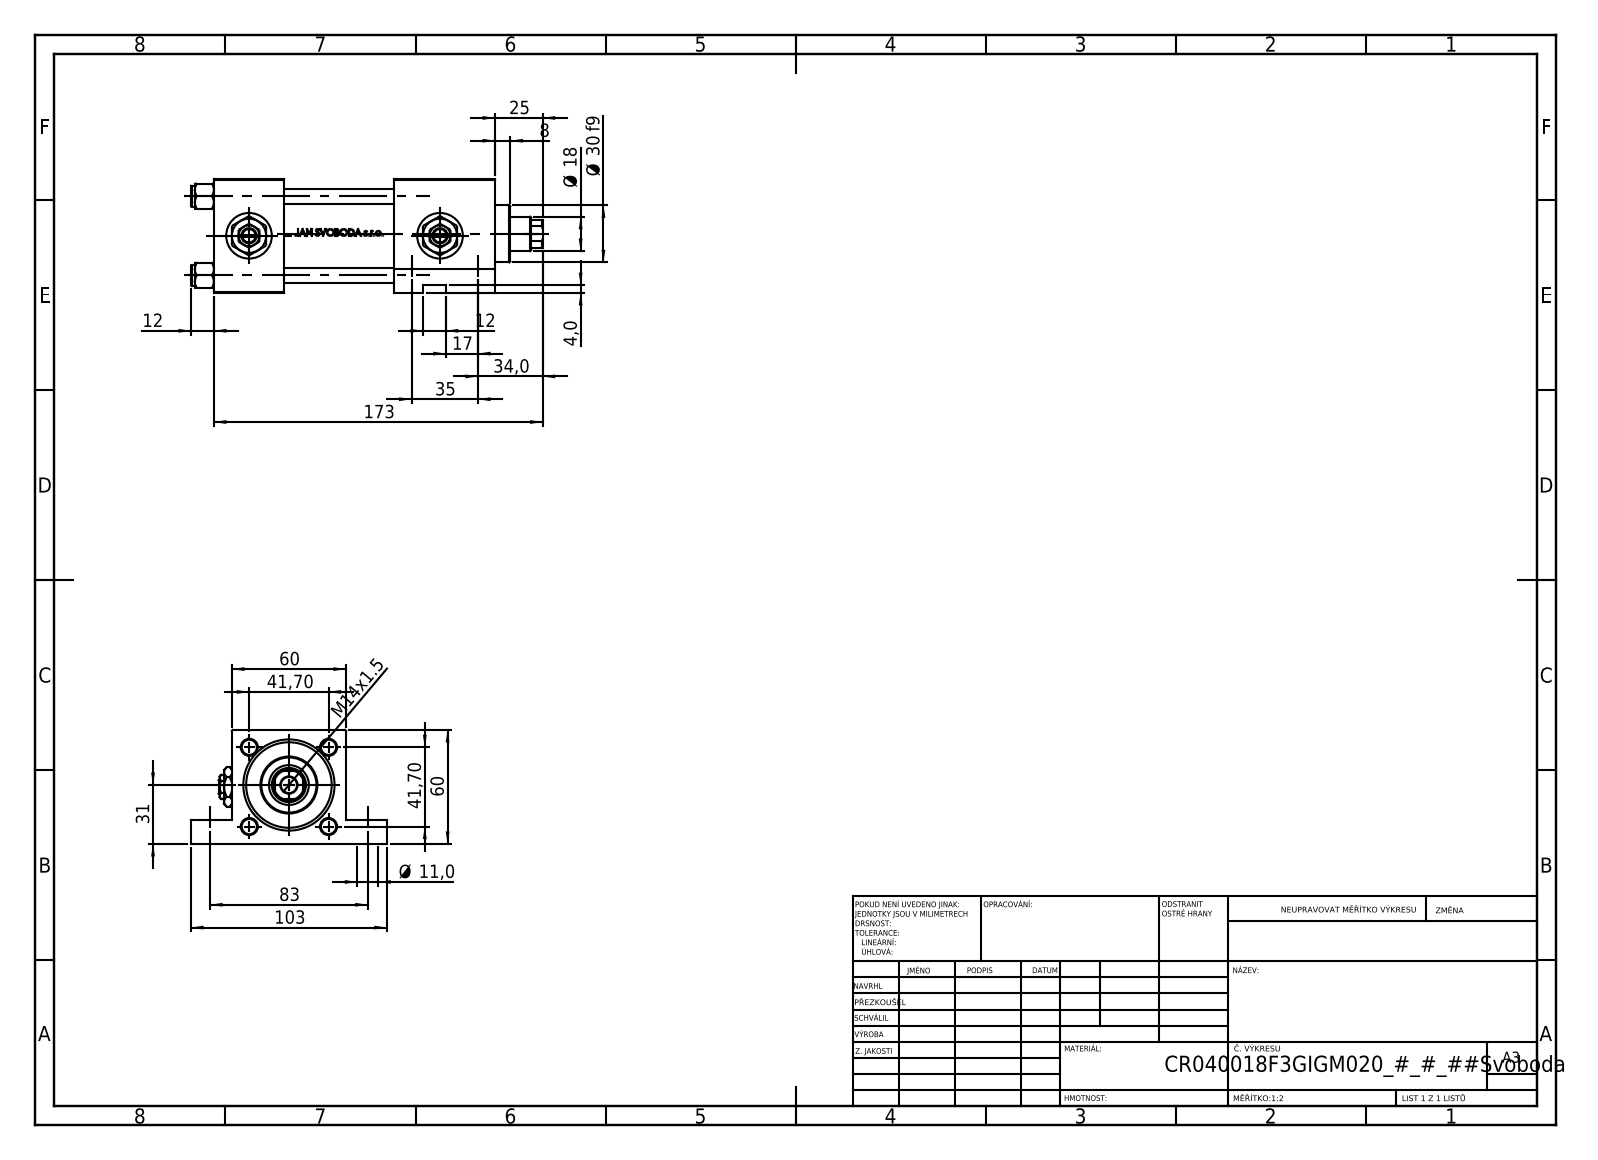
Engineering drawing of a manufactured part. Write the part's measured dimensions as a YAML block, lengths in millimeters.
part_name: "V215CR_VCP_F; V215CR_F_TYCINKA; V215_VC_A; V215CR_F_Body (+2 more)"
step_written_by: "SolidWorks 2019 (CONFIG_CONTROL_DESIGN)"
units: millimeters
bodies: {solids: 13, faces: 1215, planar: 484, cylindrical: 149, other: 582}
overall_size: [185, 103, 60]
volume: 420373
surface_area: 114469
round_holes:
  - {diameter: 8, count: 4}
  - {diameter: 16.66, count: 3}
  - {diameter: 24, count: 3}
  - {diameter: 7, count: 2}
  - {diameter: 11, count: 2}
  - {diameter: 11, count: 2}
  - {diameter: 8.5, count: 1}
  - {diameter: 16, count: 1}
  - {diameter: 18, count: 1}
  - {diameter: 21, count: 1}
  - {diameter: 31, count: 1}
  - {diameter: 40, count: 1}
round_bosses_or_shafts:
  - {diameter: 11, count: 4}
  - {diameter: 46, count: 1}
  - {diameter: 30, count: 1}
partial_cylinders:
  - {radius: 8.5, count: 1}
face_to_face_distances: [60, 37, 148, 111, 53, 58, 95, 119.3, 82.3, 24.3]
hole_center_spacings: [41.7, 28.79, 30.2, 35, 42.09, 50.06, 58.97, 83]
